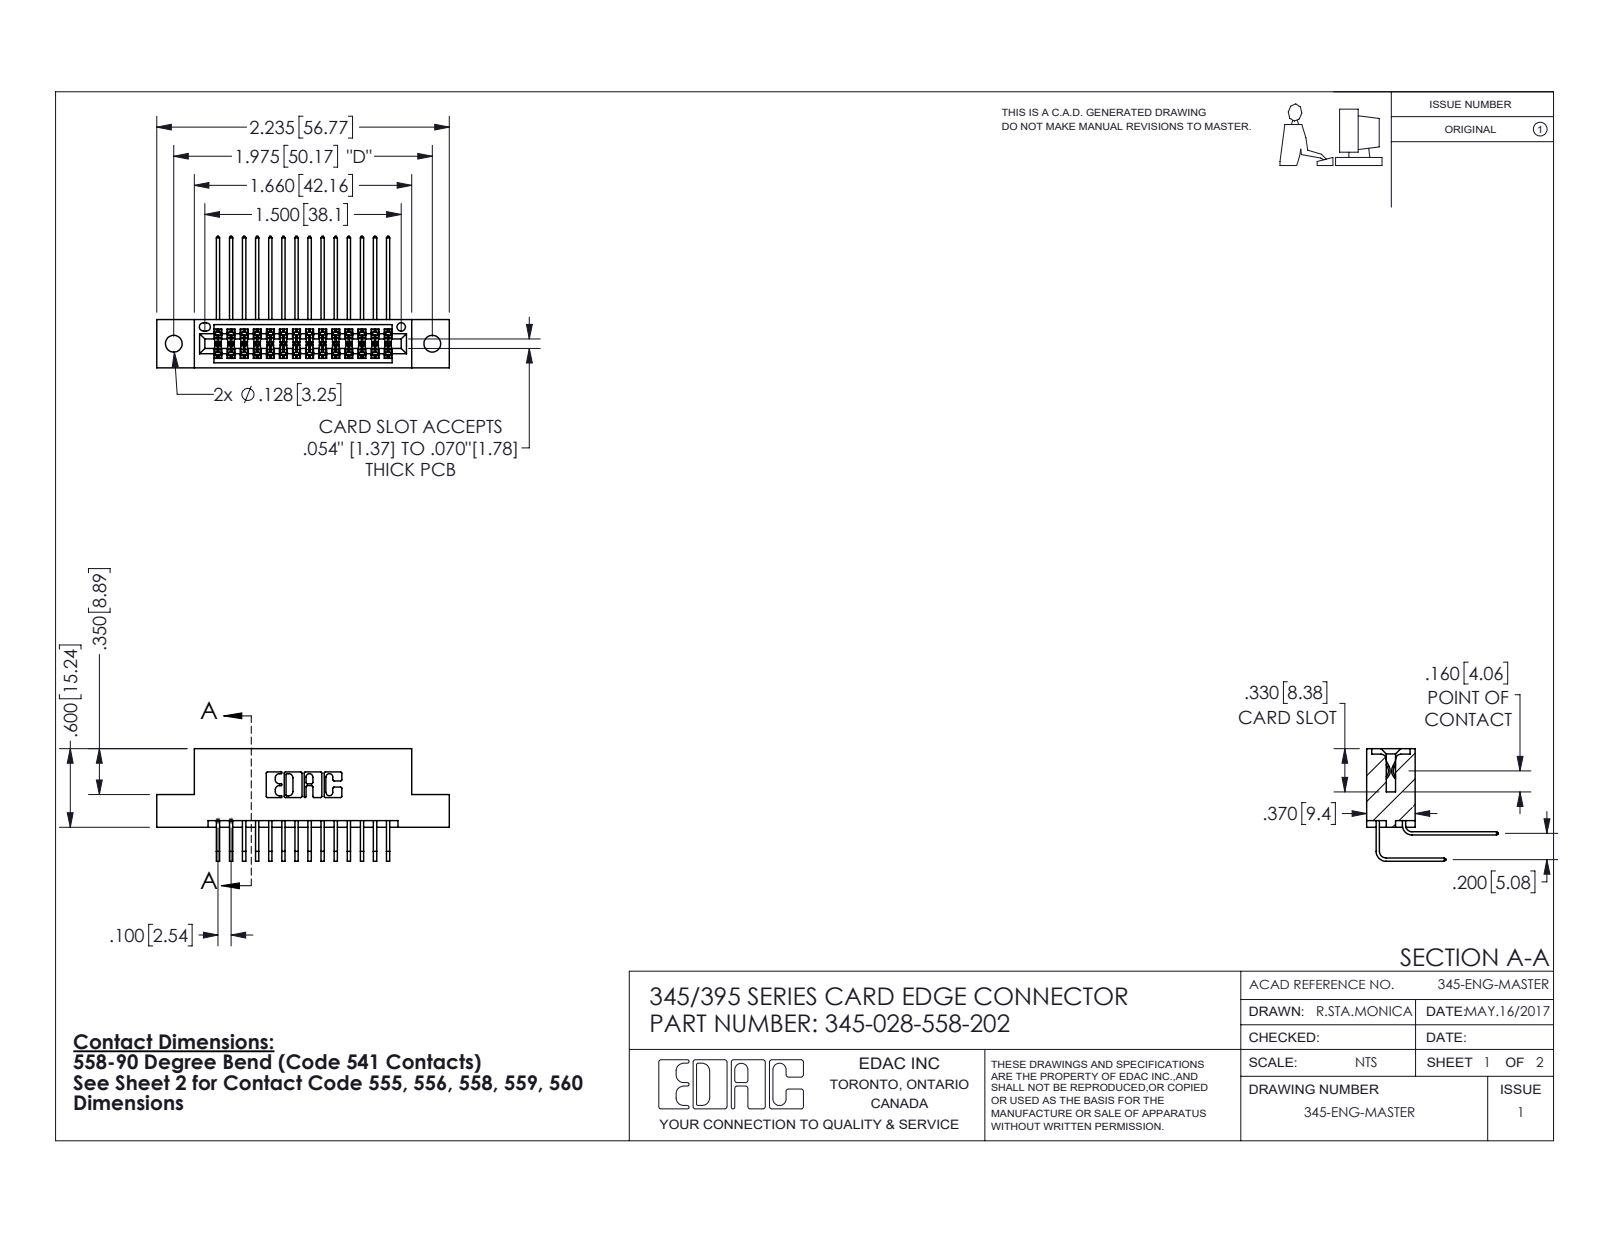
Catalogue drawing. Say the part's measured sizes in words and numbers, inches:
The part is named "345-028-558-202; 345-292-001_558 Tail - 2; 345 Part_Flush Mounting Lugs - 0.128 Dia; 345-292-001_558 559 Tail - 1". Its 3-D file was written by "SolidWorks 2016 (CONFIG_CONTROL_DESIGN)". It is 29 solids with 1582 faces: 1060 planar, 522 cylindrical and 0 other. Overall it measures 2.235 by 1.005 by 0.859 inches. Its volume is 0.328 cubic inches and its surface area 12.24 square inches. Round holes: 2 of diameter 0.128, 1 of diameter 0.064. Partial cylindrical surfaces (rounded edges, fillets, slot ends): 56 of radius 0.006, 22 of radius 0.01, 6 of radius 0.007, 6 of radius 0.031, 3 of radius 0.026, 2 of radius 0.014, 2 of radius 0.019, 2 of radius 0.022. The main face-to-face distances are 0.2, 0.072, 0.298, 0.37, 0.098, 0.272, 0.025, 0.225, 0.285, 0.1. The hole center spacings are 0.27, 1.742, 1.975.
